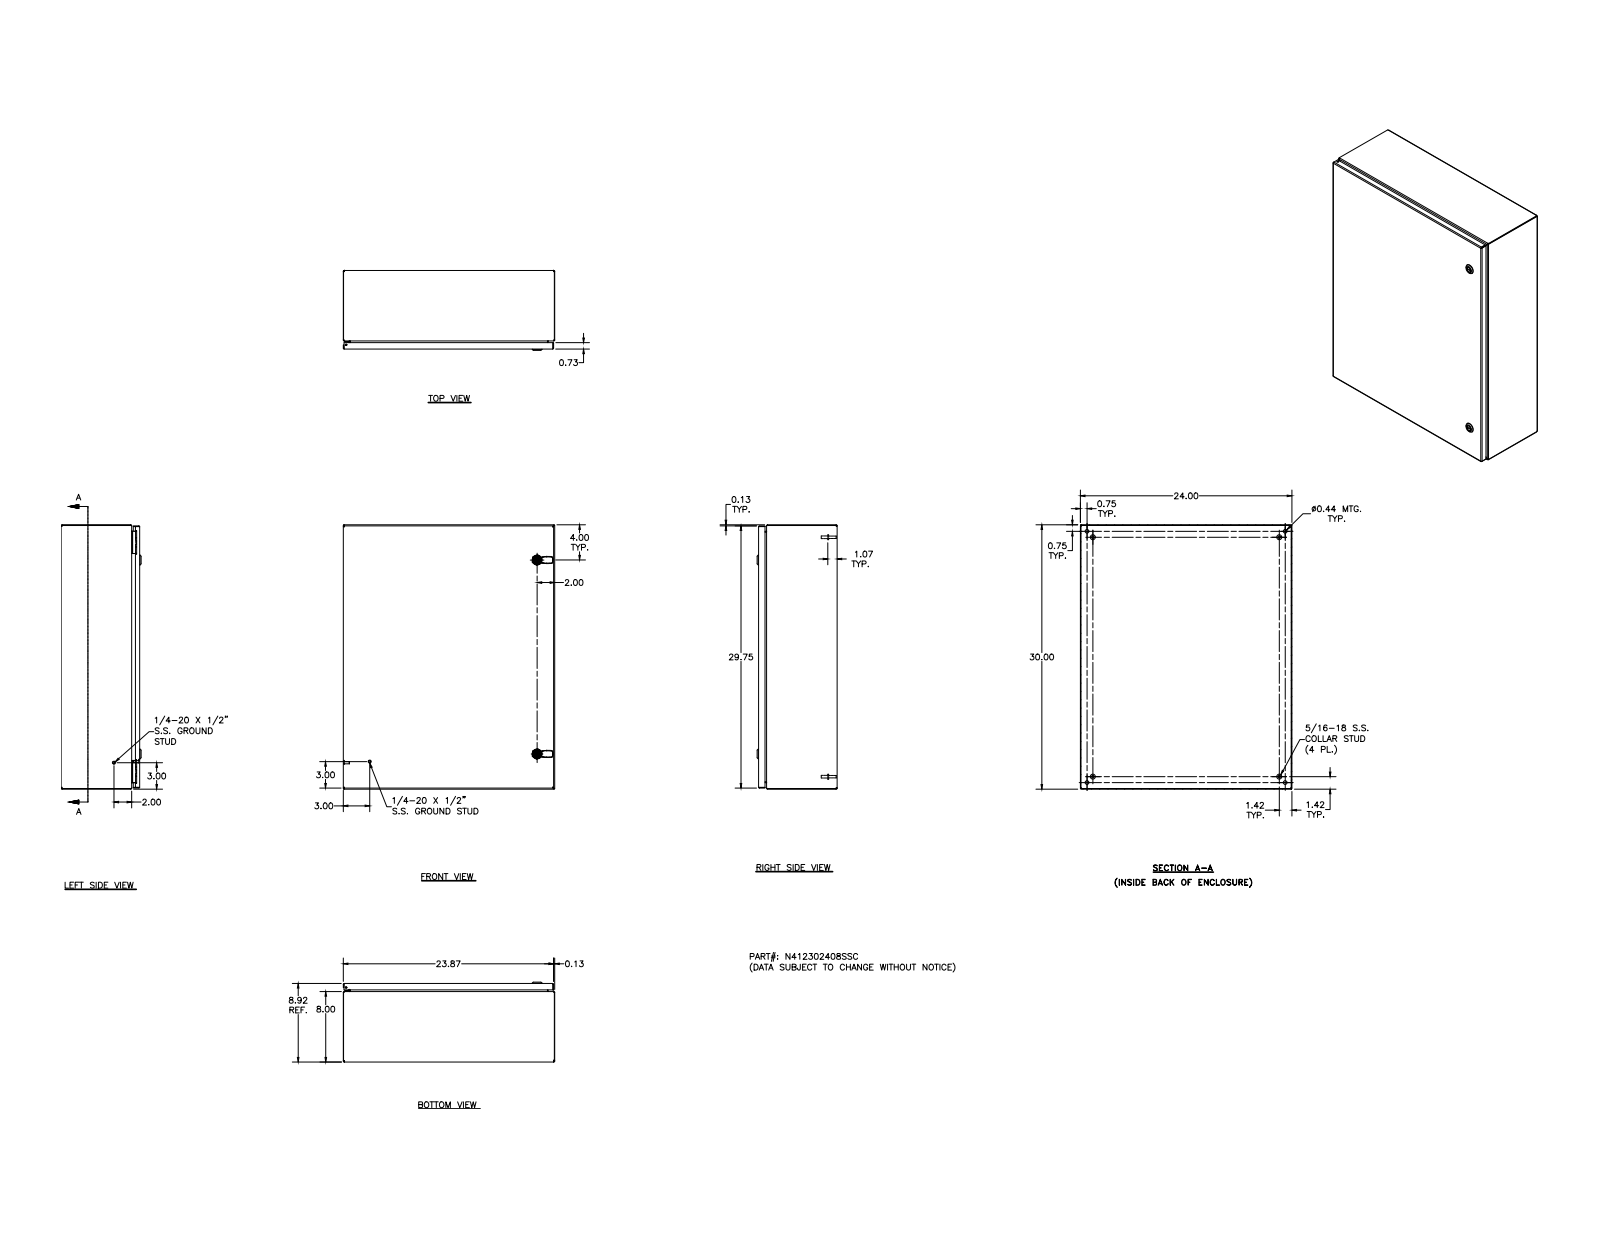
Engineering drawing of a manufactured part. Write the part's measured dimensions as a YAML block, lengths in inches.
part_name: "N412302408SSC; N412302408SSCBKP; 388151; N4123024SSCLID (+8 more)"
step_written_by: "Autodesk Inventor 2011 (AUTOMOTIVE_DESIGN)"
units: inches
bodies: {solids: 42, faces: 1682, planar: 706, cylindrical: 600, other: 376}
overall_size: [30, 24, 9.075]
volume: 186.9
surface_area: 5071
round_holes:
  - {diameter: 0.188, count: 5}
  - {diameter: 0.093, count: 4}
  - {diameter: 0.152, count: 4}
  - {diameter: 0.167, count: 4}
  - {diameter: 0.172, count: 4}
  - {diameter: 0.437, count: 4}
  - {diameter: 0.156, count: 2}
  - {diameter: 0.197, count: 2}
  - {diameter: 0.315, count: 2}
  - {diameter: 0.394, count: 2}
  - {diameter: 0.402, count: 2}
  - {diameter: 0.634, count: 2}
round_bosses_or_shafts:
  - {diameter: 0.25, count: 10}
  - {diameter: 0.563, count: 4}
  - {diameter: 0.36, count: 4}
  - {diameter: 0.32, count: 4}
  - {diameter: 0.3, count: 4}
  - {diameter: 0.275, count: 4}
  - {diameter: 0.256, count: 4}
  - {diameter: 0.164, count: 4}
partial_cylinders:
  - {radius: 0.031, count: 30}
  - {radius: 0.05, count: 26}
  - {radius: 0.105, count: 20}
  - {radius: 0.016, count: 18}
  - {radius: 0.02, count: 15}
  - {radius: 0.125, count: 14}
  - {radius: 0.032, count: 8}
  - {radius: 0.07, count: 8}
face_to_face_distances: [0.074, 8.843, 8.917, 8.769, 23.926, 29.926, 23.852, 24, 29.852, 30]
hole_center_spacings: [26, 0.017, 0.66, 22.869, 0.019, 0.5, 0.648, 0.652]
